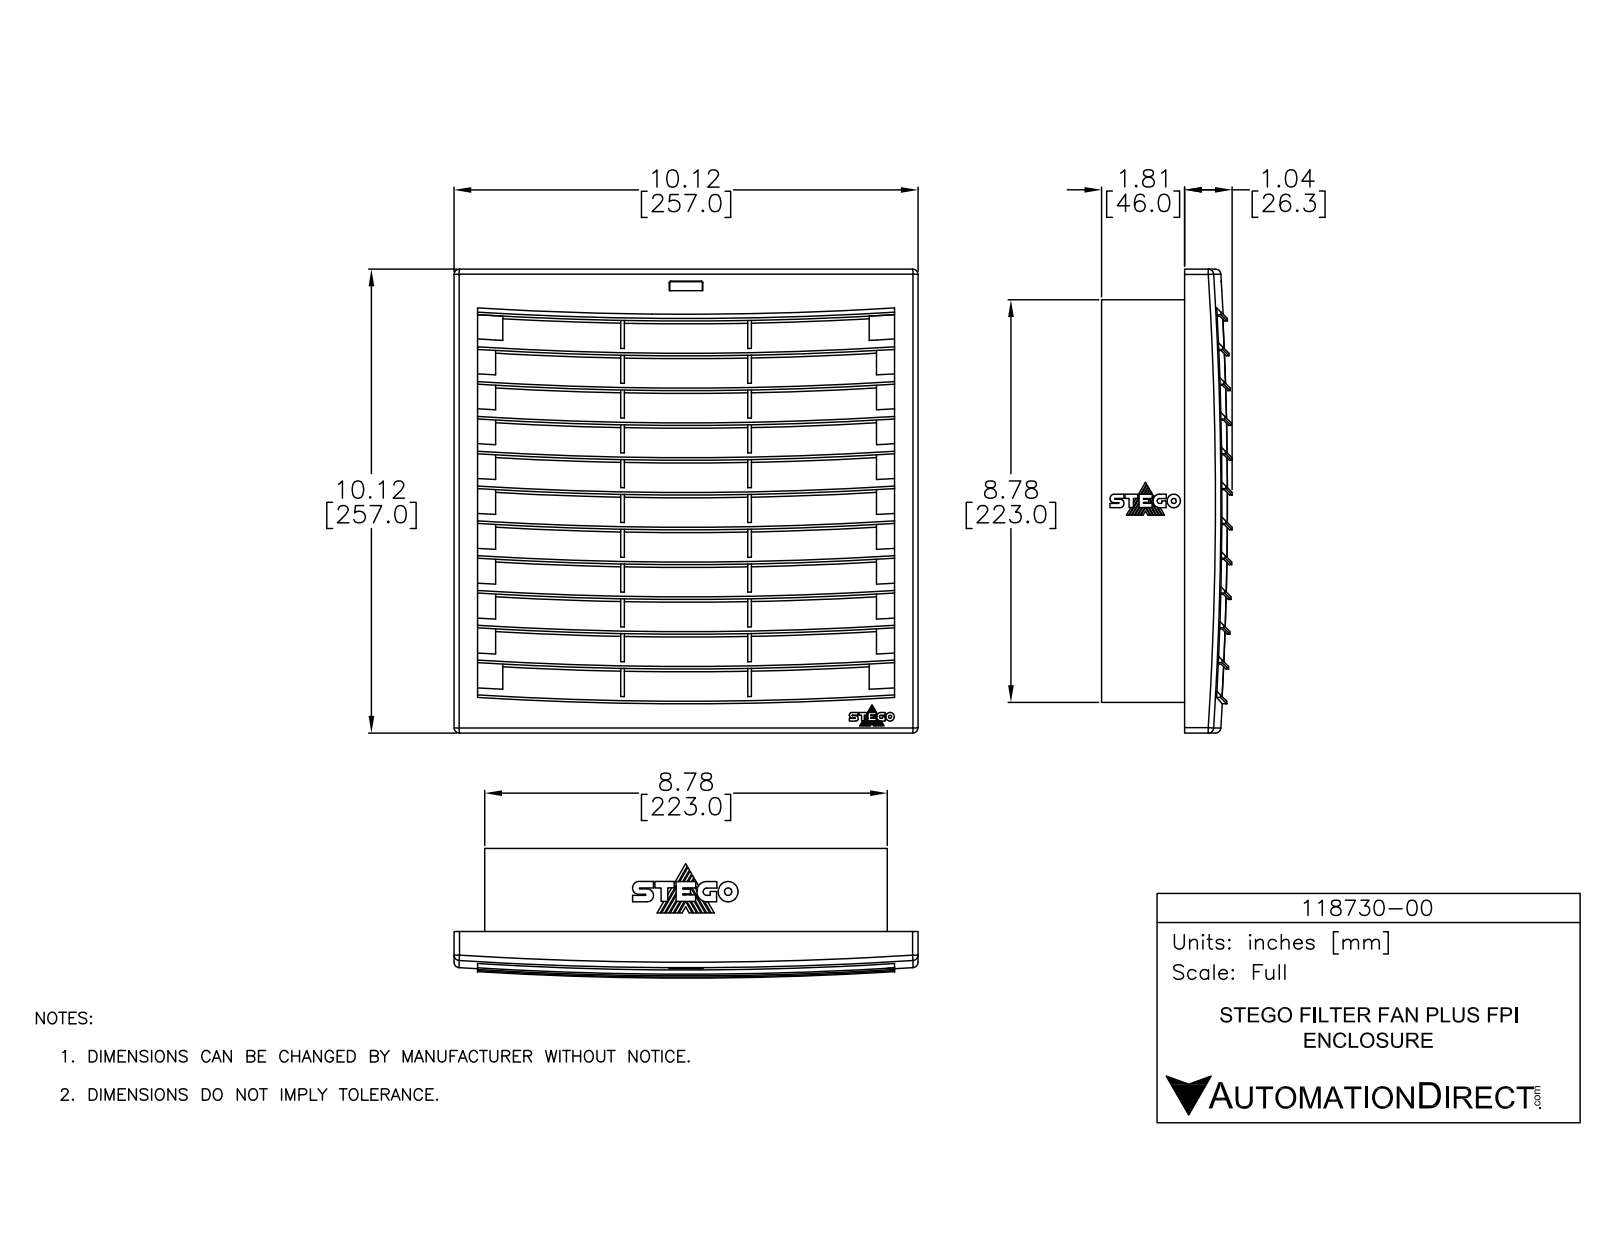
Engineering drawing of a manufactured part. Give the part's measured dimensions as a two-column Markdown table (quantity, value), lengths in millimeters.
| quantity | value |
| --- | --- |
| part name | 118730-00 |
| STEP written by | SolidWorks 2018 (AUTOMOTIVE_DESIGN) |
| units | millimeters |
| bodies | 1 solid, 572 faces (314 planar, 258 cylindrical, 0 other) |
| overall size | 257 × 257 × 72 |
| volume | 949 600 mm³ |
| surface area | 446 100 mm² |
| round holes (diameter × count) | 114 × 1, 137.7 × 1, 161.4 × 1, 189.6 × 1 |
| round bosses / shafts (diameter × count) | 170.4 × 1, 146.7 × 1, 123 × 1 |
| partial cylindrical surfaces (radius × count) | 1081.5 × 21, 5 × 4, 23.7 × 1, 33.3 × 1, 37.8 × 1, 45.1 × 1, 49.6 × 1, 799.1 × 1 |
| main face-to-face distances | 1.5, 13.6, 6.1, 18.4, 12.3, 54.5, 68.1, 40.9, 5.6, 217.4 |
